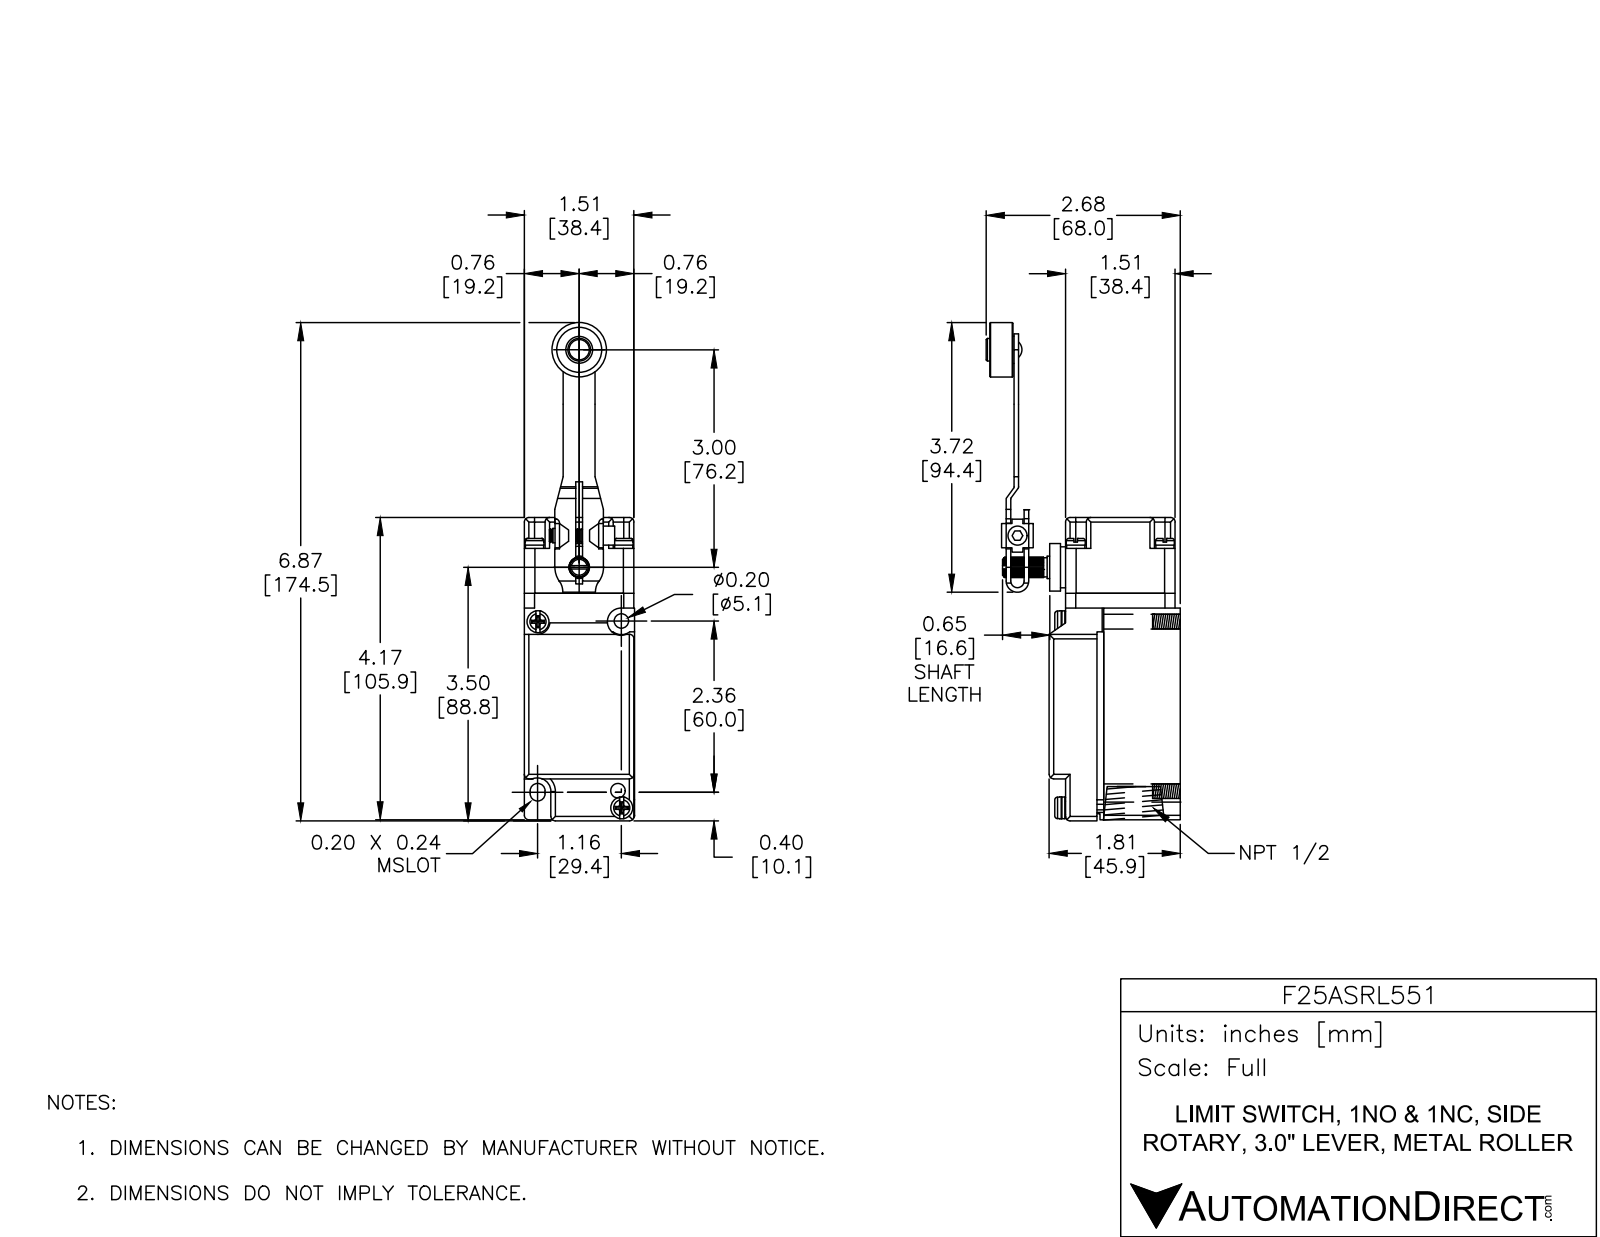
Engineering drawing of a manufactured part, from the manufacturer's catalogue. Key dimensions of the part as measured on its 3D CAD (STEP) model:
Part name (STEP PRODUCT): F25ASRL551; Imported187; Imported186; Imported184 (+8 more)
STEP written by: SolidWorks 2002296 (CONFIG_CONTROL_DESIGN)
Units: inches
Bodies: 17 solids, 927 faces (512 planar, 233 cylindrical, 182 other)
Overall size (bounding box): 6.872 × 2.678 × 1.52
Volume: 10.39 in³ · Surface area: 75.27 in²
Round holes (diameter × count): ⌀0.177 ×4, ⌀0.19 ×3, ⌀0.2 ×3, ⌀0.156 ×1, ⌀0.17 ×1, ⌀0.25 ×1, ⌀0.5 ×1, ⌀0.58 ×1
Round bosses / shafts (diameter × count): ⌀0.26 ×4, ⌀0.25 ×4, ⌀0.302 ×2, ⌀0.3 ×2, ⌀0.75 ×1, ⌀0.655 ×1, ⌀0.565 ×1, ⌀0.375 ×1
Partial cylindrical surfaces — rounded edges, fillets, slot ends (radius × count): R0.062 ×29, R0.03 ×16, R0.015 ×8, R0.145 ×8, R0.063 ×4, R0.14 ×4, R0.032 ×3, R0.025 ×2
Main face-to-face distances: 0.094, 1.149, 1.055, 1.52, 0.66, 0.754, 1.809, 1.51, 0.063, 0.227
Hole centre spacings: 1.23, 1.23, 1.74, 2.815, 0.225, 0.235, 0.936, 0.942
